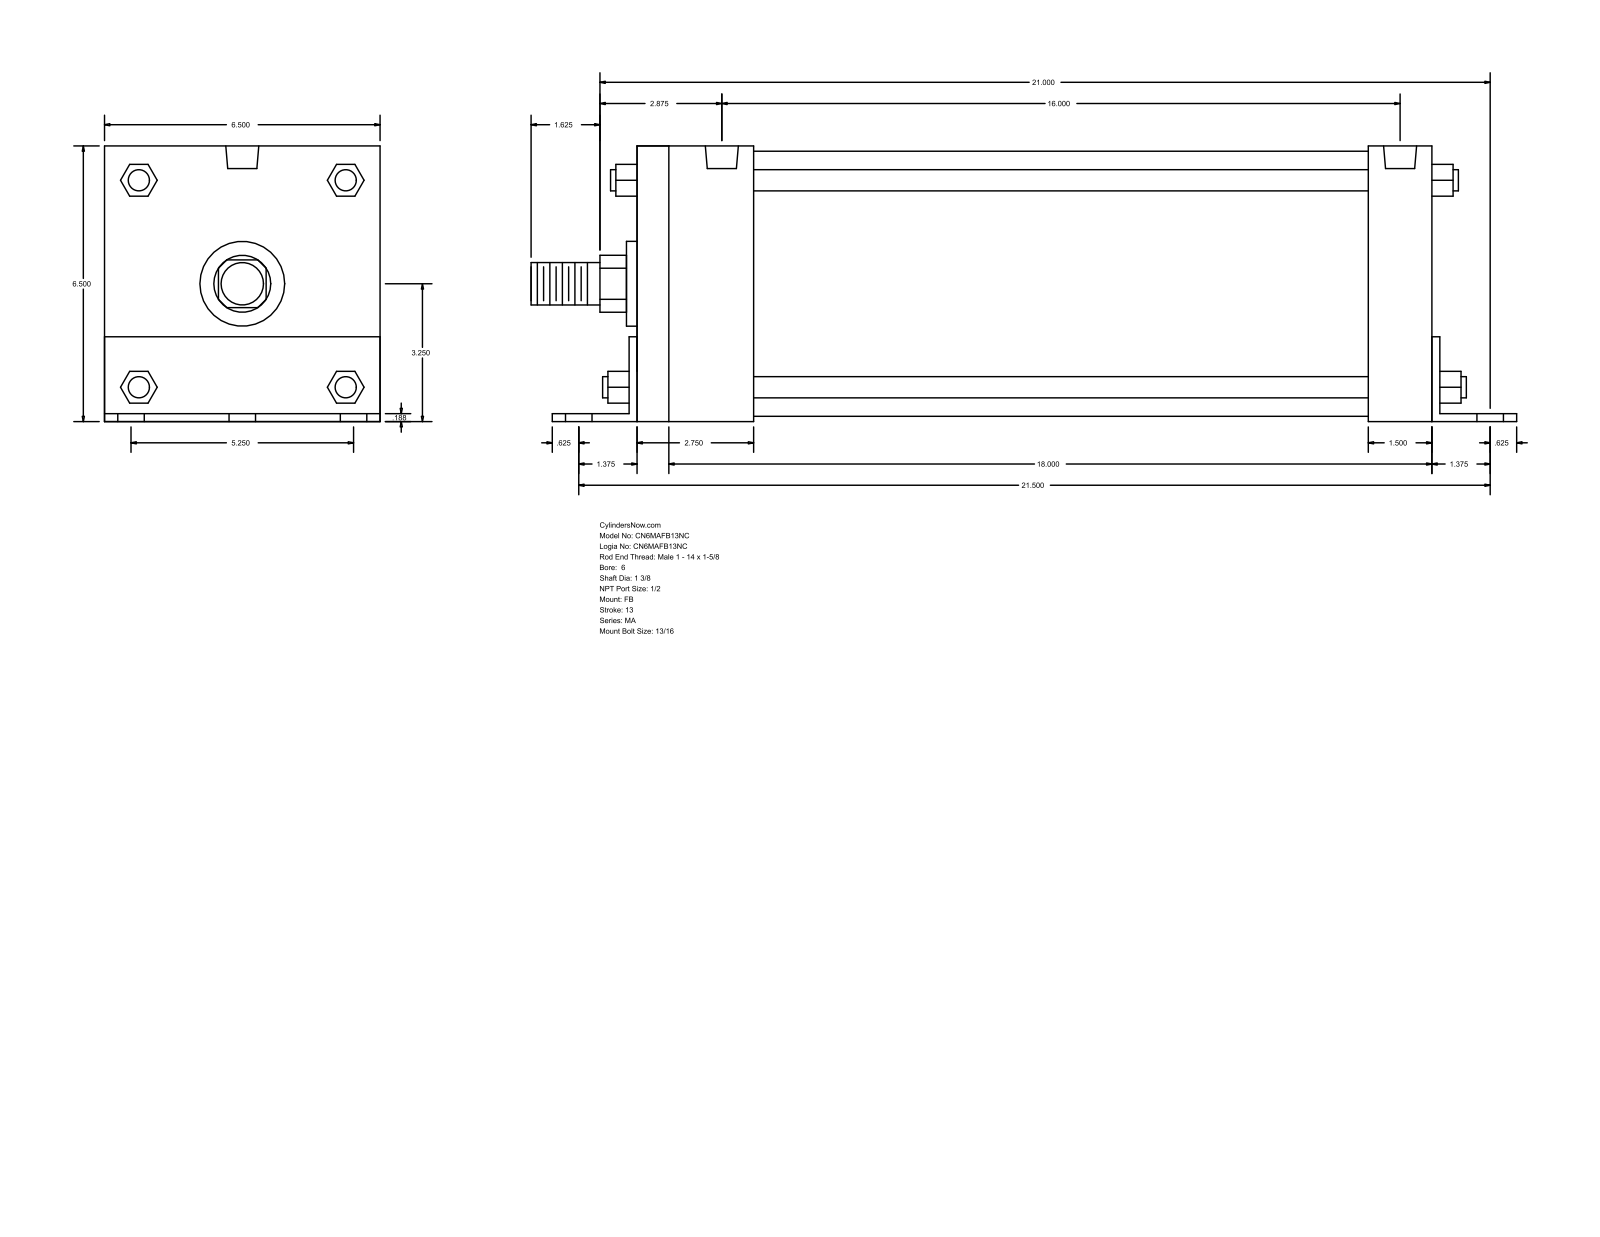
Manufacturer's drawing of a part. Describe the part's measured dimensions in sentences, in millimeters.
The part is named "MA_FB__0600_1.375". Its 3-D file was written by "GSSL Pune (CONFIG_CONTROL_DESIGN)". It is 0 solids with 140 faces: 105 planar, 35 cylindrical and 0 other. Overall it measures 587.38 by 165.15 by 165.1 millimeters. Round holes: 6 of diameter 20.64, 4 of diameter 17.46, 2 of diameter 19.77. Round bosses or shafts: 4 of diameter 12.7, 1 of diameter 158.75, 1 of diameter 50.8, 1 of diameter 34.92, 1 of diameter 25.4. Partial cylindrical surfaces (rounded edges, fillets, slot ends): 1 of radius 17.06, 1 of radius 32.05. The main face-to-face distances are 165.1, 4.76, 473.07, 165.15, 4.71, 160.39, 4.77, 38.1, 42.86, 482.6. The hole center spacings are 66.67, 547.01, 542.93, 83.82, 85.78, 108.6, 133.34, 403.22.
